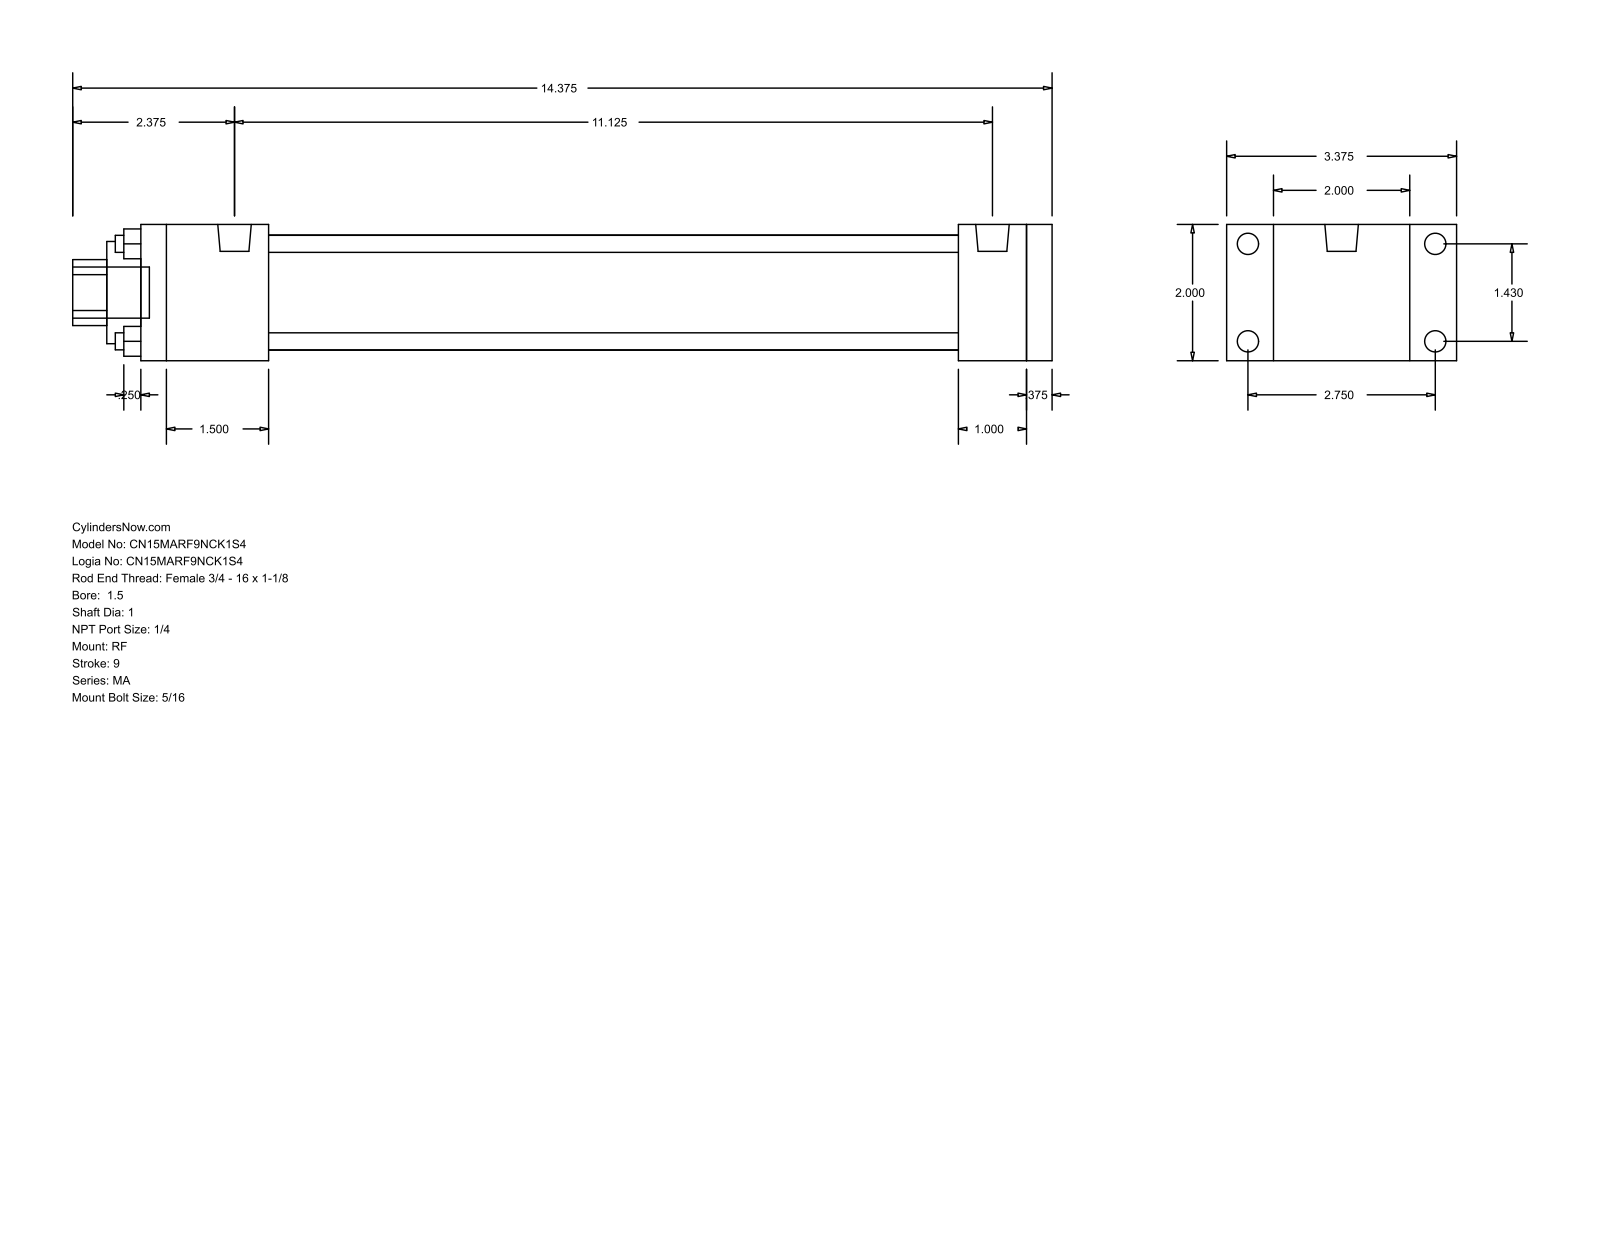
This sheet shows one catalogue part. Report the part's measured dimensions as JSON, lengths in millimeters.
{"part_name": "MA_RF__0150_1", "step_written_by": "GSSL Pune (CONFIG_CONTROL_DESIGN)", "units": "millimeters", "bodies": {"solids": 0, "faces": 92, "planar": 64, "cylindrical": 28, "other": 0}, "overall_size": [365.12, 85.72, 50.8], "round_holes": [[6.35, 4], [25.4, 1], [38.1, 1], [42.93, 1]], "round_bosses_or_shafts": [[7.94, 8], [12.49, 2], [19.05, 1]], "partial_cylinders_radius": [[12.29, 1]], "face_to_face_distances": [50.8, 9.52, 339.72, 330.2, 25.4, 304.8, 34.92, 47.63, 257.17, 282.57], "hole_center_spacings": [25.68, 36.32, 51.36]}
